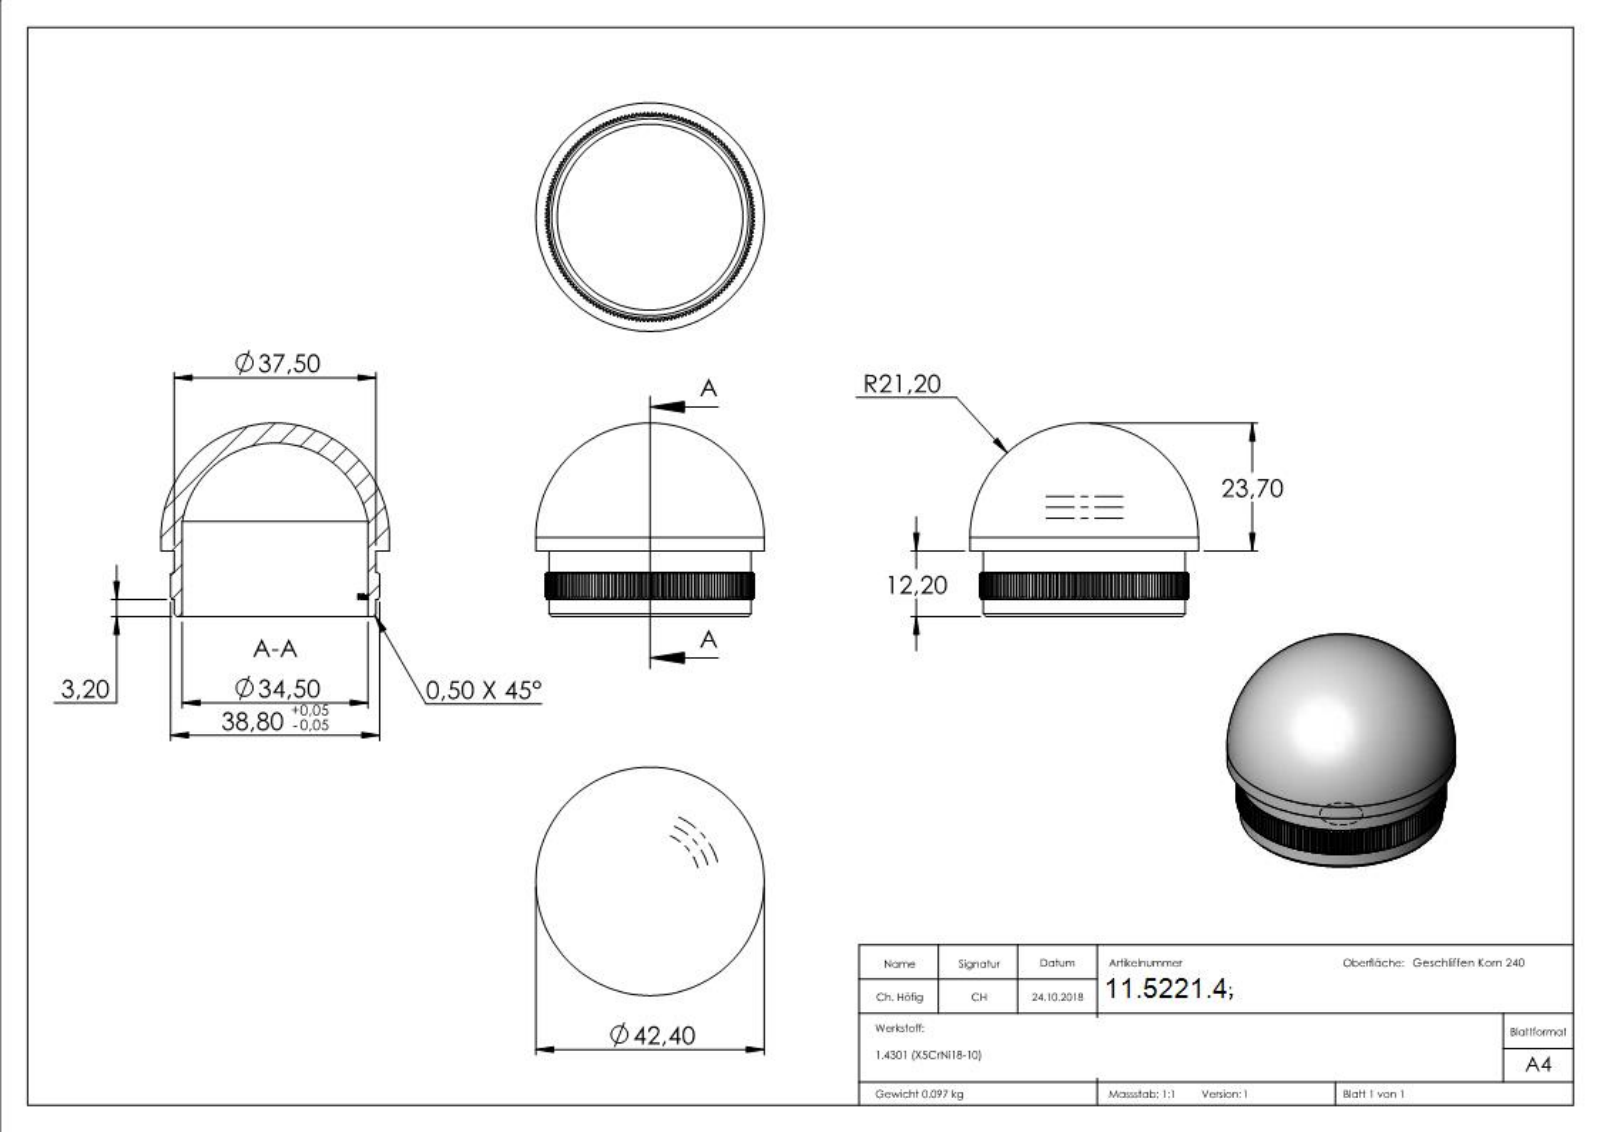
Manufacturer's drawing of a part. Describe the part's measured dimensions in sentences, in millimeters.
The part is named "50270-240G". Its 3-D file was written by "SolidWorks 2015 (CONFIG_CONTROL_DESIGN)". It is 1 solid with 1097 faces: 449 planar, 205 cylindrical and 443 other. Overall it measures 42.4 by 42.4 by 35.9 millimeters. Its volume is 12 293 cubic millimeters and its surface area 9 119 square millimeters. Round holes: 1 of diameter 34.5. Round bosses or shafts: 1 of diameter 42.4, 1 of diameter 37.5. Partial cylindrical surfaces (rounded edges, fillets, slot ends): 1 of radius 17.35, 1 of radius 19.4. The main face-to-face distances are 18.9, 12.2, 18.92, 18.88, 3.2, 9, 8.2, 5, 4, 1.06.
